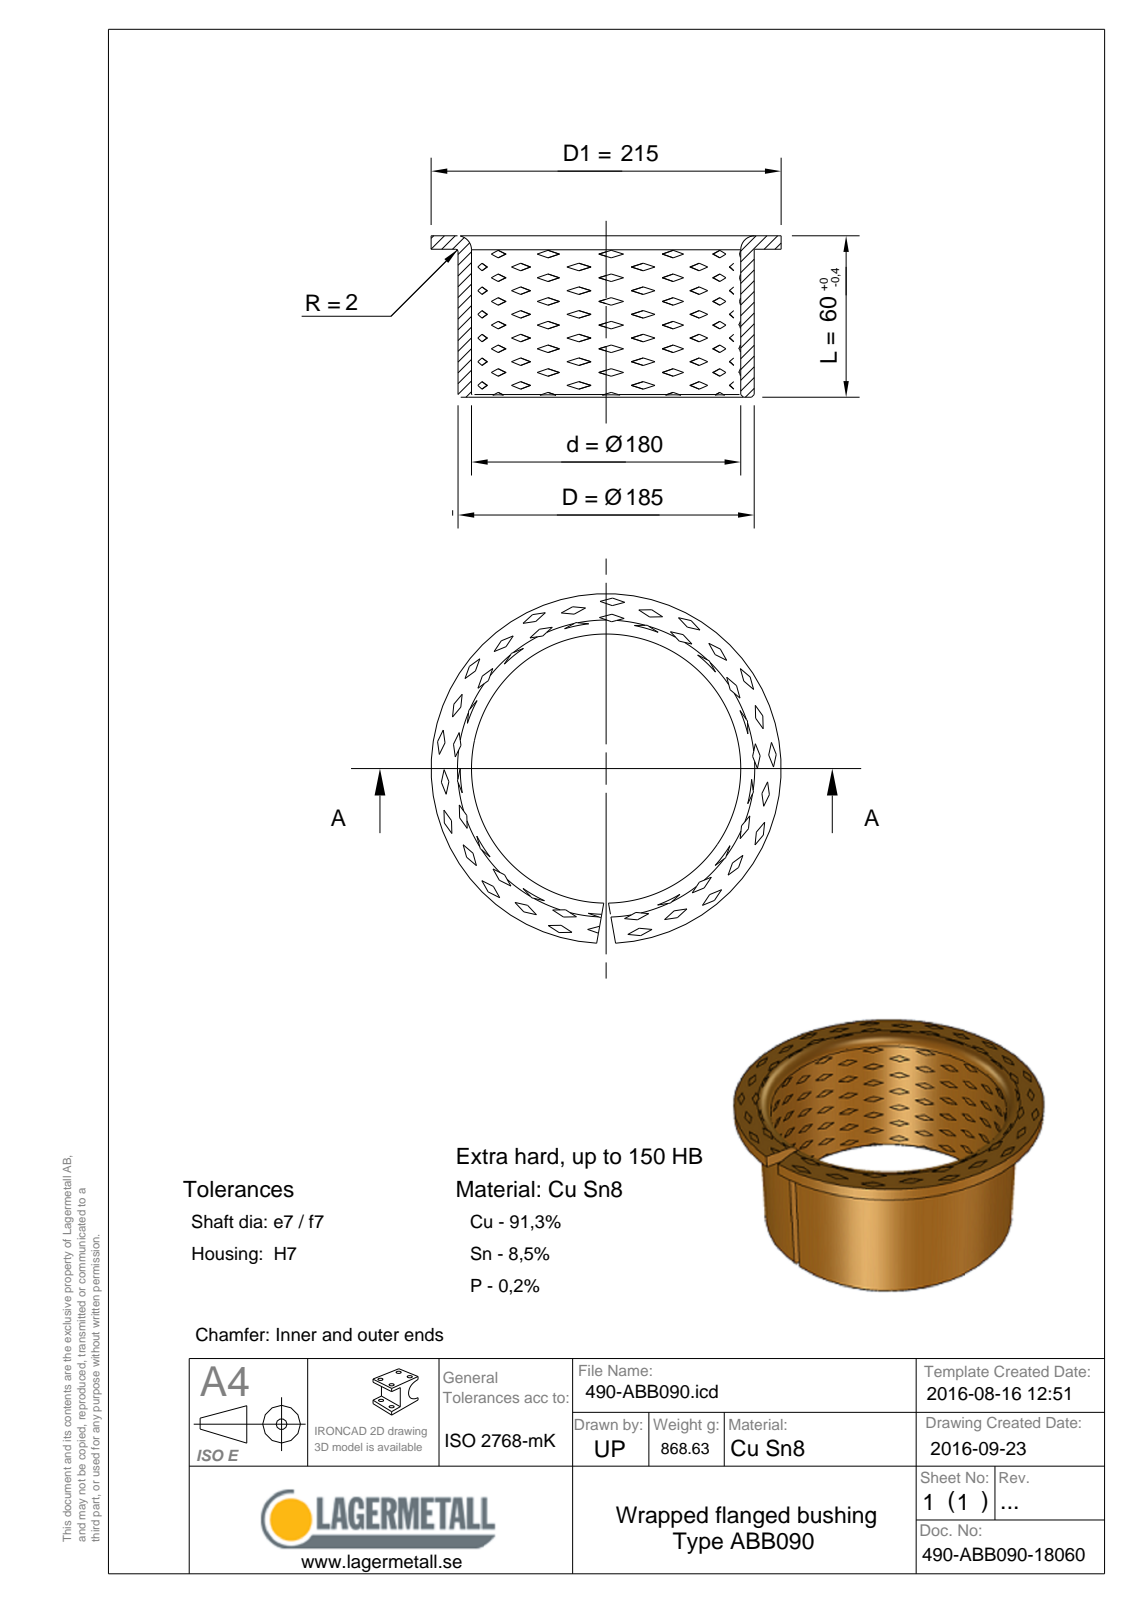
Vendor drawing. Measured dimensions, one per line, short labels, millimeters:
written by: Spatial InterOp 3D (CONFIG_CONTROL_DESIGN)
unit: mm
bodies: 1 solid, 26 faces (5 planar, 9 cylindrical, 12 other)
size: 215 × 215 × 60
volume: 107 239 mm³; area: 89 036 mm²
holes: 1× ⌀180
bosses: 1× ⌀215, 1× ⌀185
face distances: 2.5, 57.5, 60
